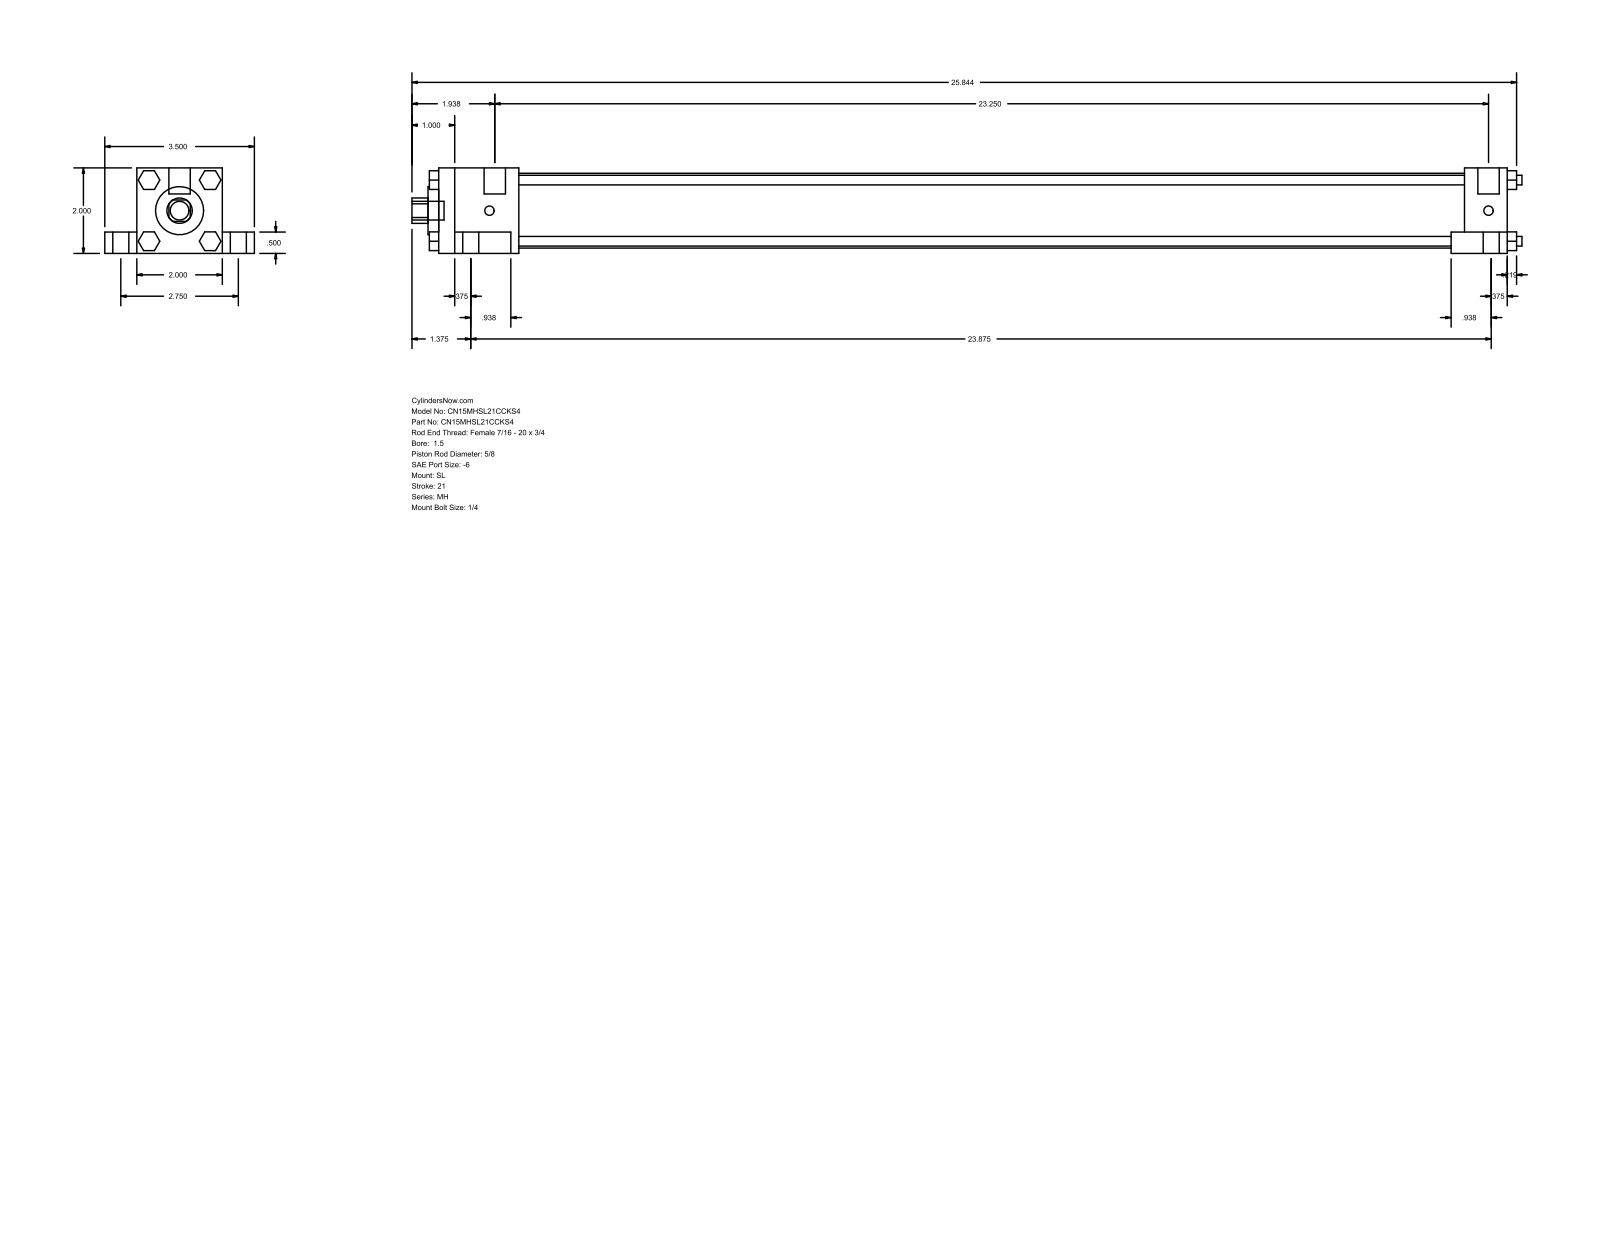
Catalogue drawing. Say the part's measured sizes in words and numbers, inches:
The part is named "MH_SL__0150_0.625". Its 3-D file was written by "GSSL Pune (CONFIG_CONTROL_DESIGN)". It is 0 solids with 148 faces: 112 planar, 36 cylindrical and 0 other. Overall it measures 25.969 by 3.5 by 2 inches. Round holes: 1 of diameter 0.625, 1 of diameter 1.125, 1 of diameter 1.75. Round bosses or shafts: 4 of diameter 0.625, 4 of diameter 0.375, 4 of diameter 0.225, 4 of diameter 0.219, 2 of diameter 0.5, 1 of diameter 0.437. Partial cylindrical surfaces (rounded edges, fillets, slot ends): 1 of radius 0.297. The main face-to-face distances are 2, 1.5, 0.75, 0.5, 2.75, 25, 0.375, 1, 1.313, 23.313.
